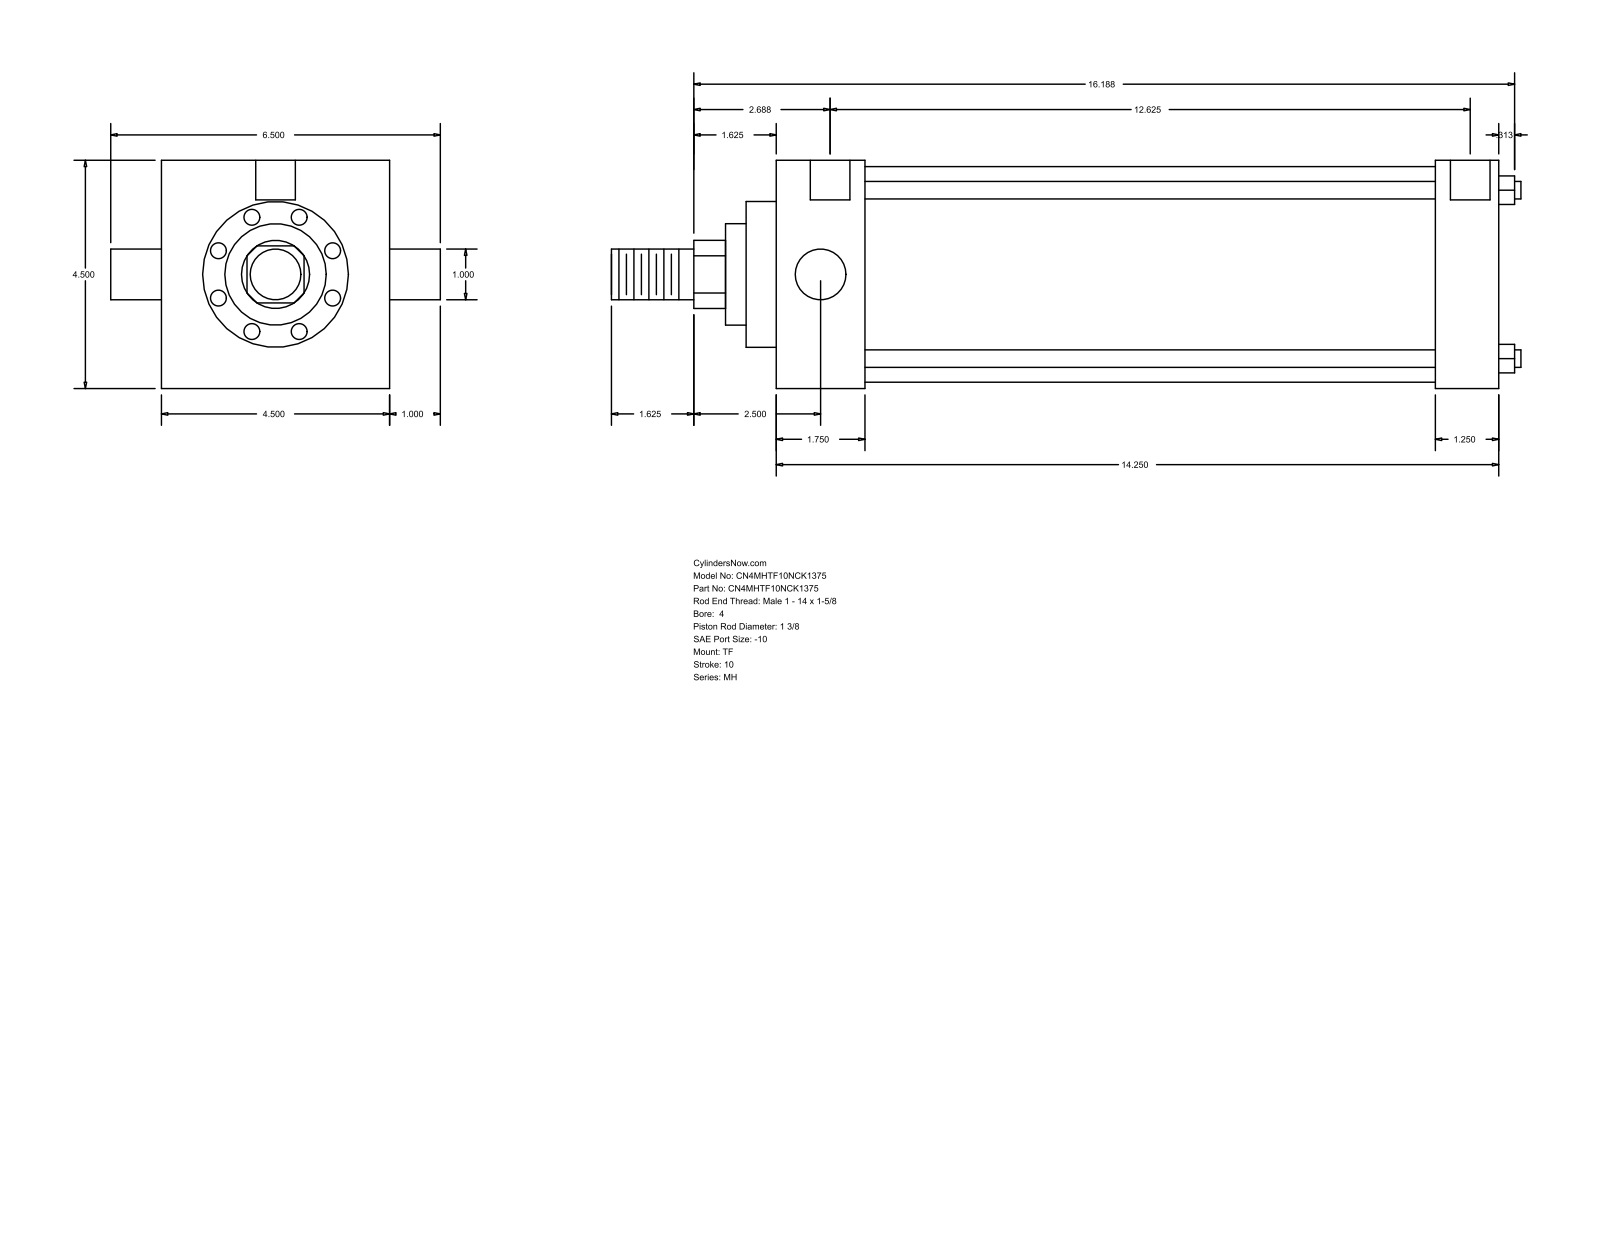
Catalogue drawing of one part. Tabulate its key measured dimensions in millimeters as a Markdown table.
| quantity | value |
| --- | --- |
| part name | MH_TF__0400_1.375 |
| STEP written by | GSSL Pune (CONFIG_CONTROL_DESIGN) |
| units | millimeters |
| bodies | 0 solids, 86 faces (61 planar, 25 cylindrical, 0 other) |
| overall size | 455.61 × 165.1 × 114.3 |
| round holes (diameter × count) | 8.73 × 3, 19.84 × 2 |
| round bosses / shafts (diameter × count) | 8.76 × 4, 25.4 × 2, 107.95 × 1, 73.03 × 1, 50.8 × 1, 34.92 × 1 |
| partial cylindrical surfaces (radius × count) | 17.06 × 1 |
| main face-to-face distances | 114.3, 361.96, 44.45, 317.51, 330.21, 285.76, 31.75, 15.08, 59.53, 345.29 |
| hole center spacings | 1.58, 1.59, 320.68, 322.26, 322.27, 323.85 |
